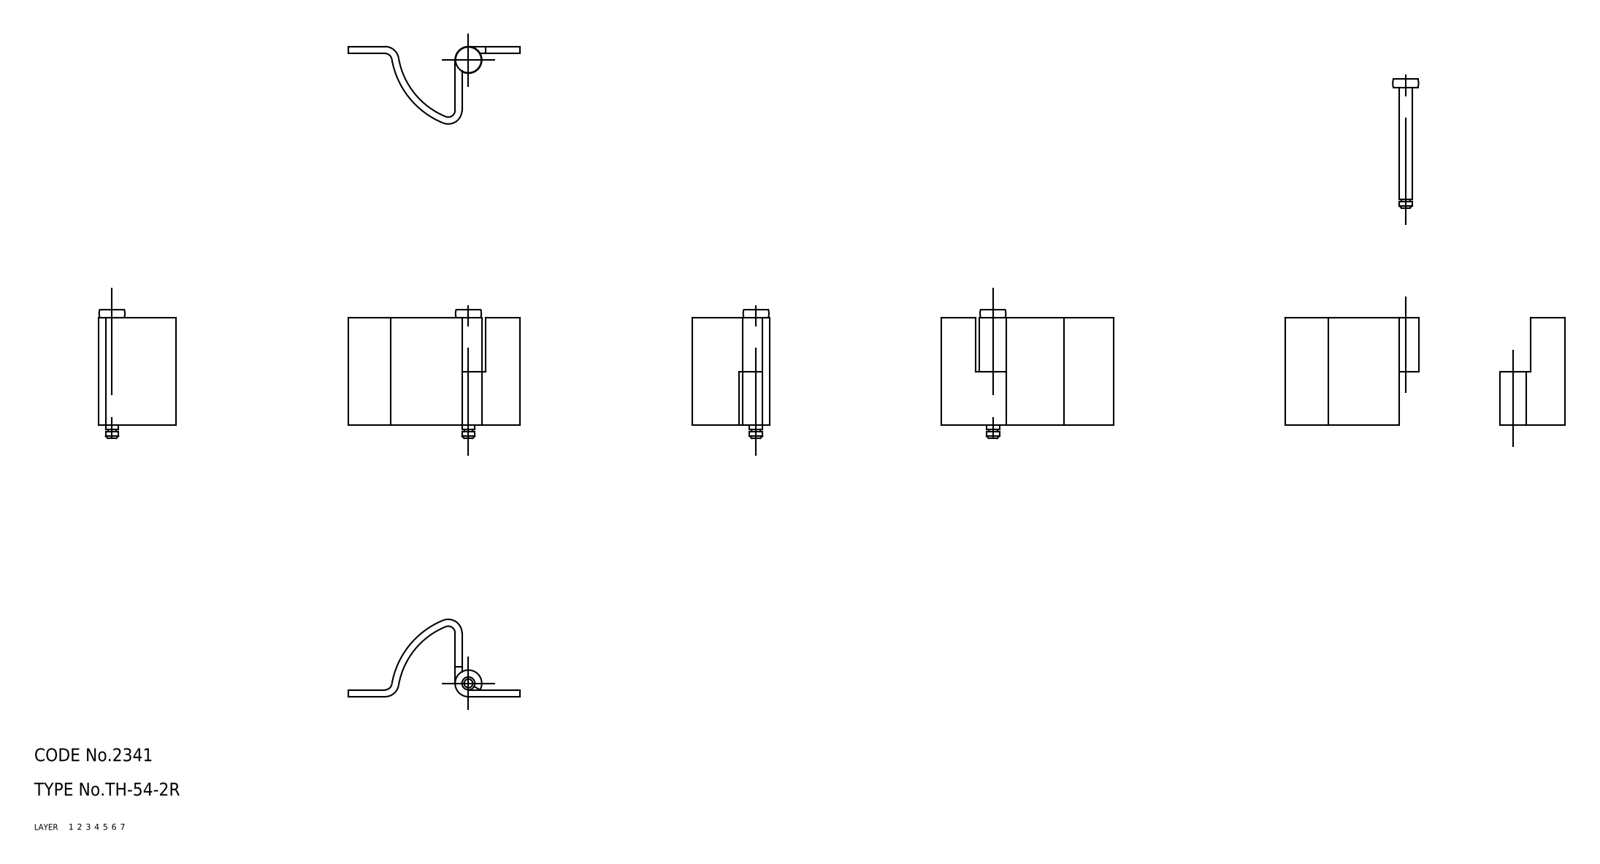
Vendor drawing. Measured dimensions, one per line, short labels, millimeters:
name: hinge piece_A_mr; hinge piece_B_mr; shaft; TH_54_2_R_11038_36
written by: CADfix (AUTOMOTIVE_DESIGN)
unit: mm
bodies: 3 solids, 42 faces (0 planar, 0 cylindrical, 42 other)
size: 40 × 30 × 18
volume: 2 947 mm³; area: 4 153 mm²
